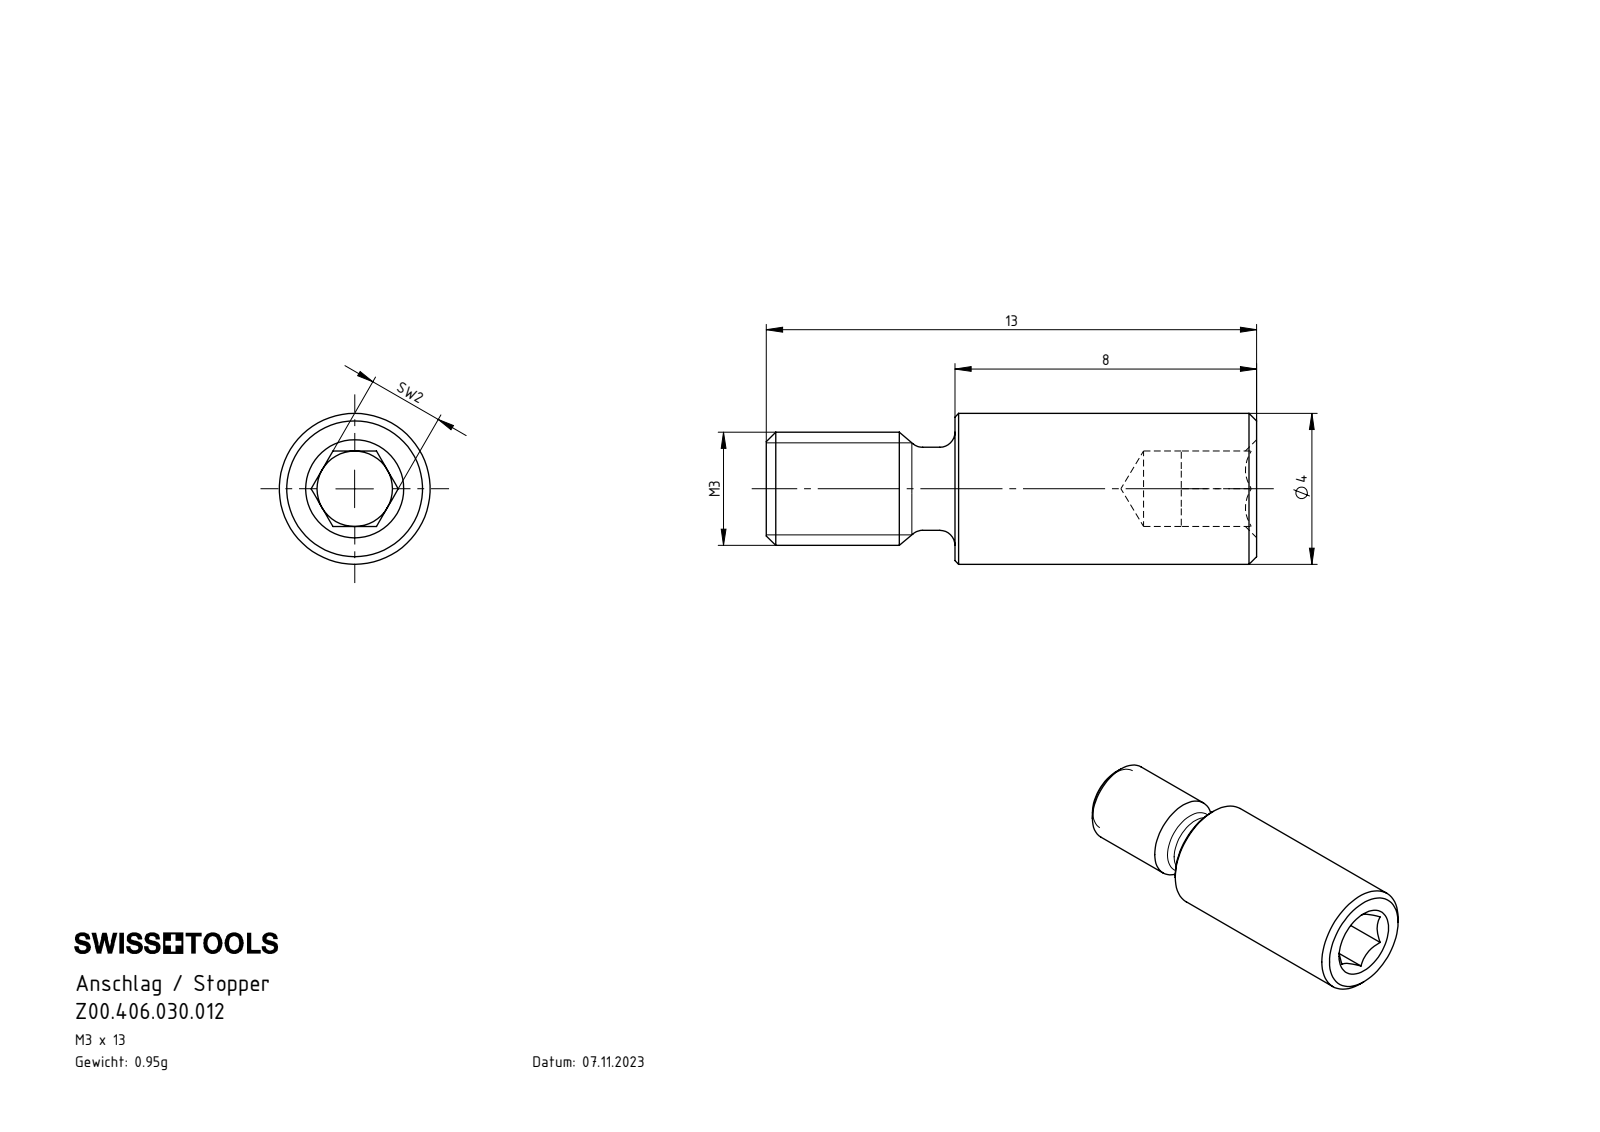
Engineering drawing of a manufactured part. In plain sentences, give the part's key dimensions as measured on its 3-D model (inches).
The part is named "Z00.406.030.012". Its 3-D file was written by "SolidWorks 2022 (AUTOMOTIVE_DESIGN)". It is 1 solid with 39 faces: 15 planar, 8 cylindrical and 16 other. Overall it measures 0.512 by 0.157 by 0.157 inches. Its volume is 0.007 cubic inches and its surface area 0.293 square inches. Round holes: 1 of diameter 0.079. Round bosses or shafts: 1 of diameter 0.157, 1 of diameter 0.118, 1 of diameter 0.087. The main face-to-face distances are 0.079, 0.512, 0.197, 0.315, 0.433, 0.236.
